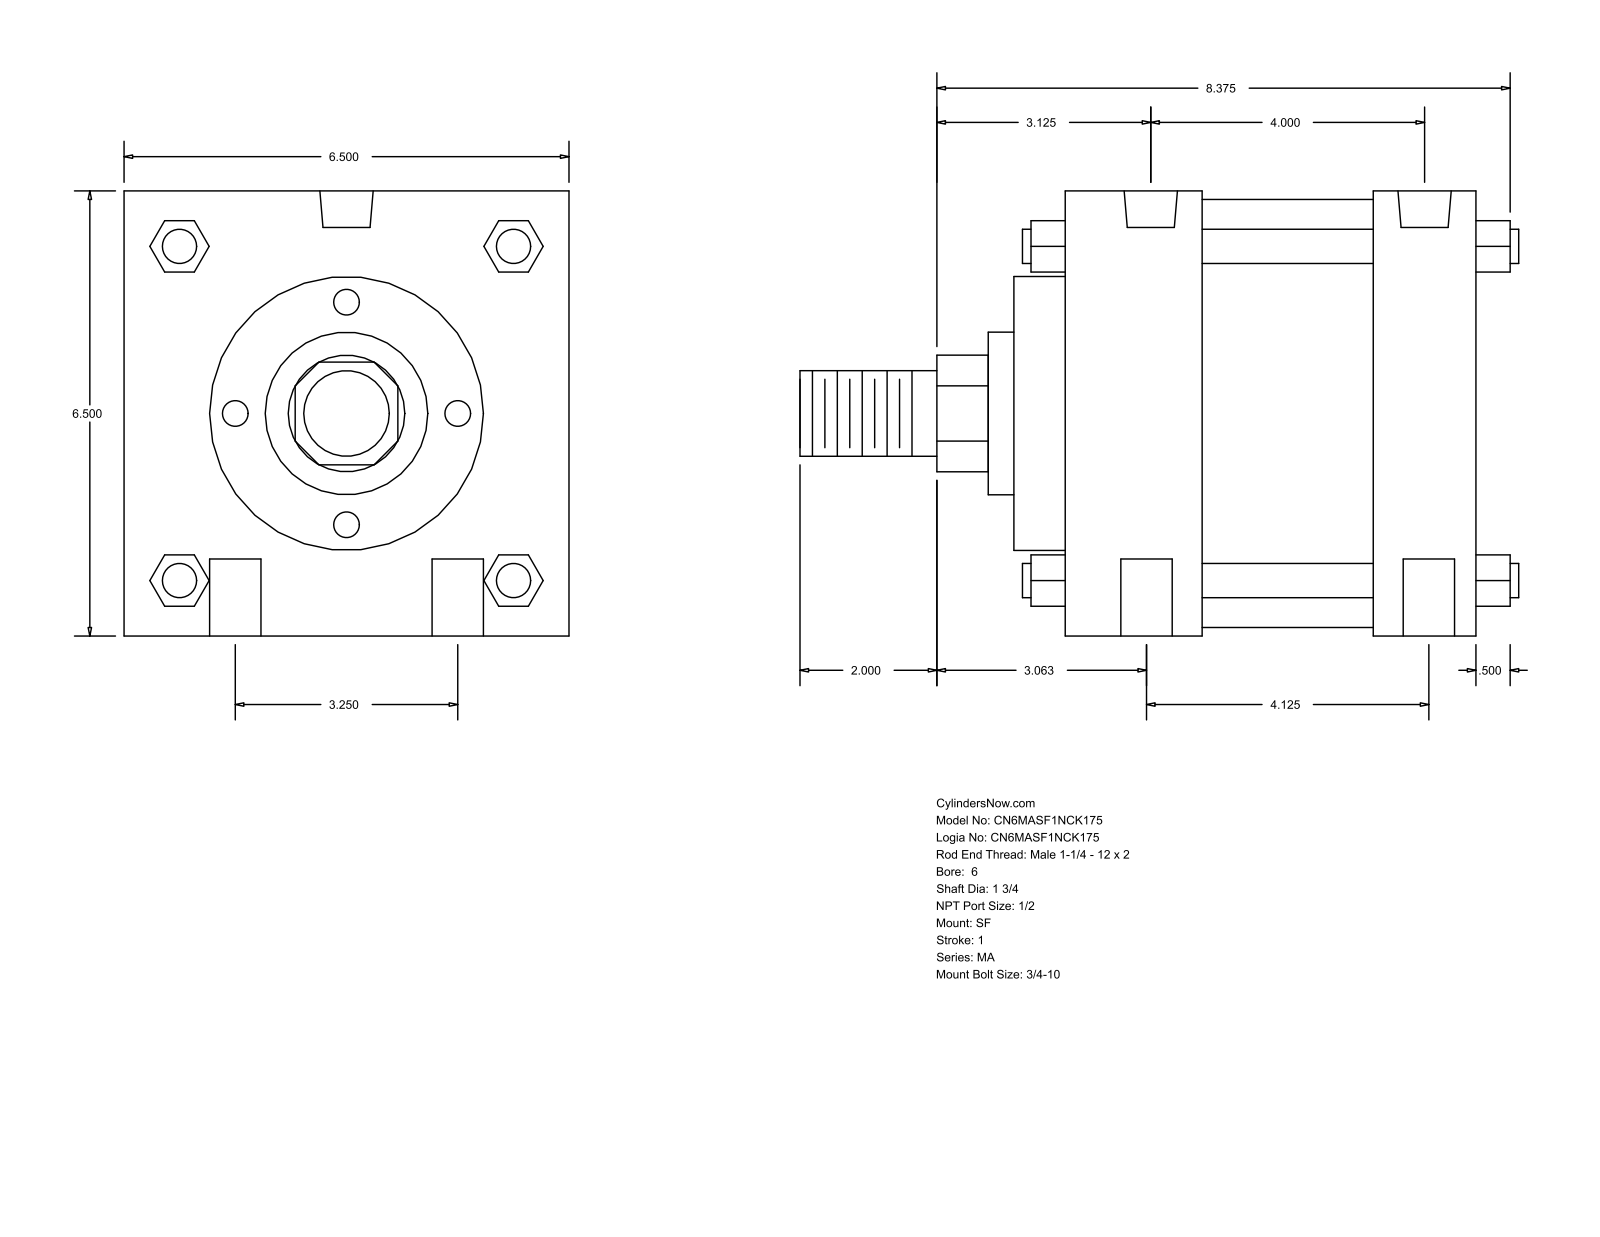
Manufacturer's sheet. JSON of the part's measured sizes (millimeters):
{"part_name": "MA_SF__0600_1.75", "step_written_by": "GSSL Pune (CONFIG_CONTROL_DESIGN)", "units": "millimeters", "bodies": {"solids": 0, "faces": 126, "planar": 95, "cylindrical": 31, "other": 0}, "overall_size": [266.7, 165.1, 165.1], "round_holes": [[19.05, 4], [17.46, 2], [19.77, 2]], "round_bosses_or_shafts": [[12.7, 4], [158.75, 1], [101.6, 1], [60.33, 1], [44.45, 1], [31.75, 1]], "partial_cylinders_radius": [[21.63, 1]], "face_to_face_distances": [165.1, 152.41, 19.05, 50.8, 38.1, 114.31, 63.51, 101.61, 69.85, 133.36], "hole_center_spacings": [41.3, 111.13, 82.54, 101.59, 104.77, 133.38]}
